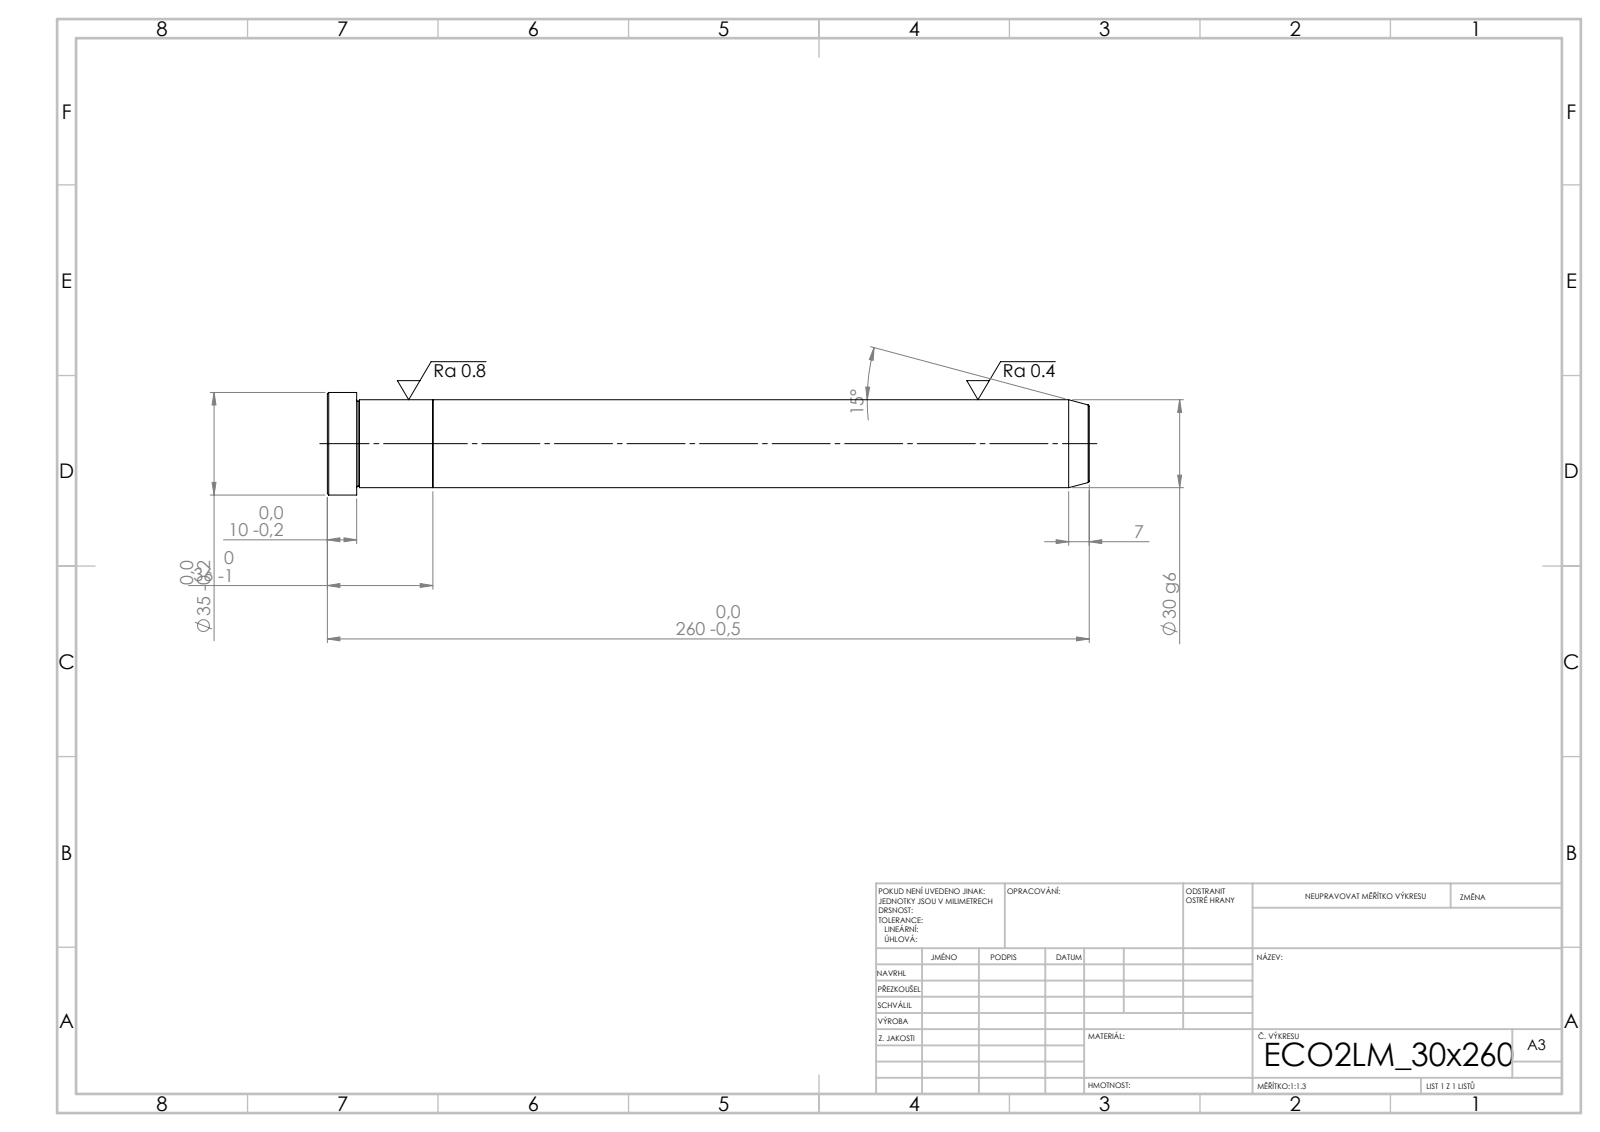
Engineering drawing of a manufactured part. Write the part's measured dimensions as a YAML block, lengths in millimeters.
step_written_by: "SolidWorks 2019 (CONFIG_CONTROL_DESIGN)"
units: millimeters
bodies: {solids: 2, faces: 21, planar: 5, cylindrical: 6, other: 10}
overall_size: [260, 35, 35]
volume: 185690
surface_area: 27823
round_bosses_or_shafts:
  - {diameter: 35, count: 1}
  - {diameter: 30, count: 1}
face_to_face_distances: [36, 224, 260, 250, 26, 10]
